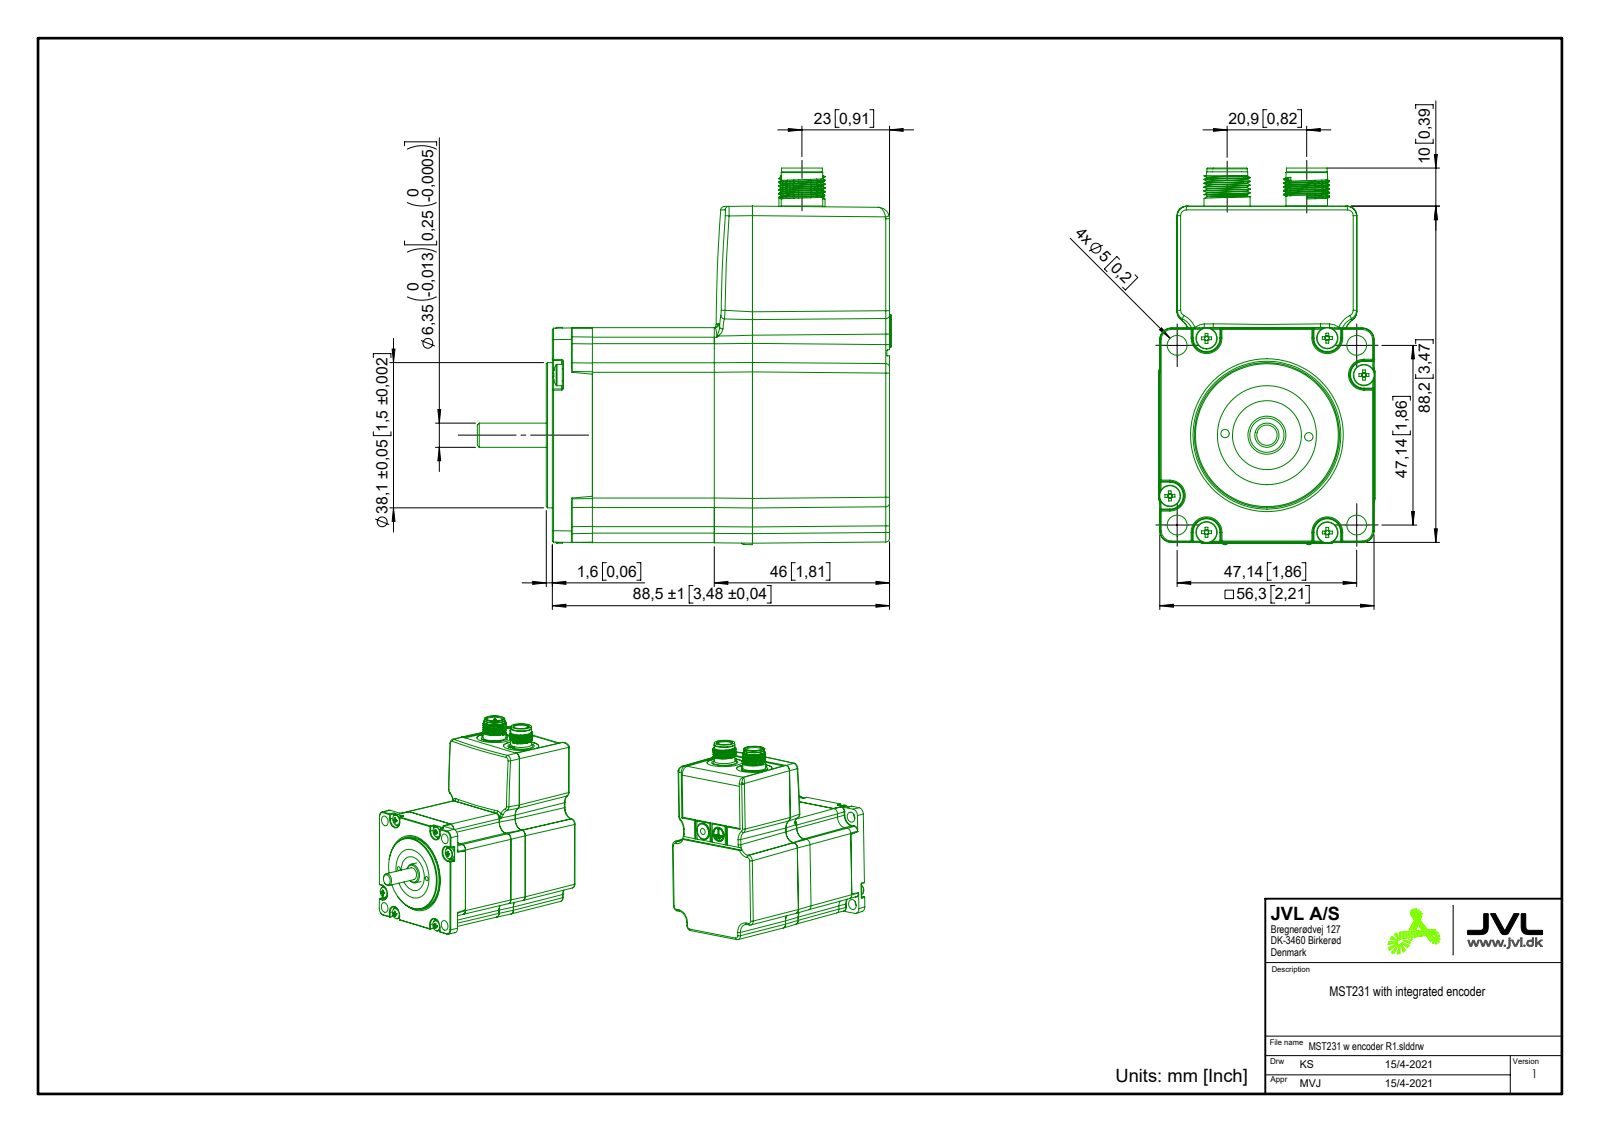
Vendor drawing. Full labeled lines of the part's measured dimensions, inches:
Part name (STEP PRODUCT): MST231 w encoder R1
STEP written by: SolidWorks 2020 (AUTOMOTIVE_DESIGN)
Units: inches
Bodies: 1 solid, 1210 faces (378 planar, 304 cylindrical, 528 other)
Overall size (bounding box): 4.28 × 3.891 × 2.231
Volume: 19.53 in³ · Surface area: 56.13 in²
Round holes (diameter × count): ⌀0.043 ×8, ⌀0.098 ×6, ⌀0.087 ×2, ⌀0.728 ×2, ⌀0.13 ×1, ⌀0.266 ×1, ⌀0.323 ×1, ⌀0.327 ×1, ⌀0.713 ×1, ⌀1.024 ×1
Round bosses / shafts (diameter × count): ⌀0.031 ×8, ⌀0.22 ×6, ⌀0.118 ×6, ⌀0.039 ×5, ⌀1.5 ×1, ⌀0.476 ×1, ⌀0.476 ×1, ⌀0.429 ×1
Partial cylindrical surfaces — rounded edges, fillets, slot ends (radius × count): R0.008 ×34, R0.098 ×29, R0.197 ×18, R0.012 ×16, R0.039 ×11, R0.091 ×8, R0.118 ×5, R0.031 ×4
Main face-to-face distances: 2.22, 0.187, 3.484, 0.028, 3.457, 2.044, 2.231, 0.063, 3.547, 3.52
Hole centre spacings: 0.108, 1.181, 0.108, 1.67, 0.091, 0.166, 2.362, 0.092
